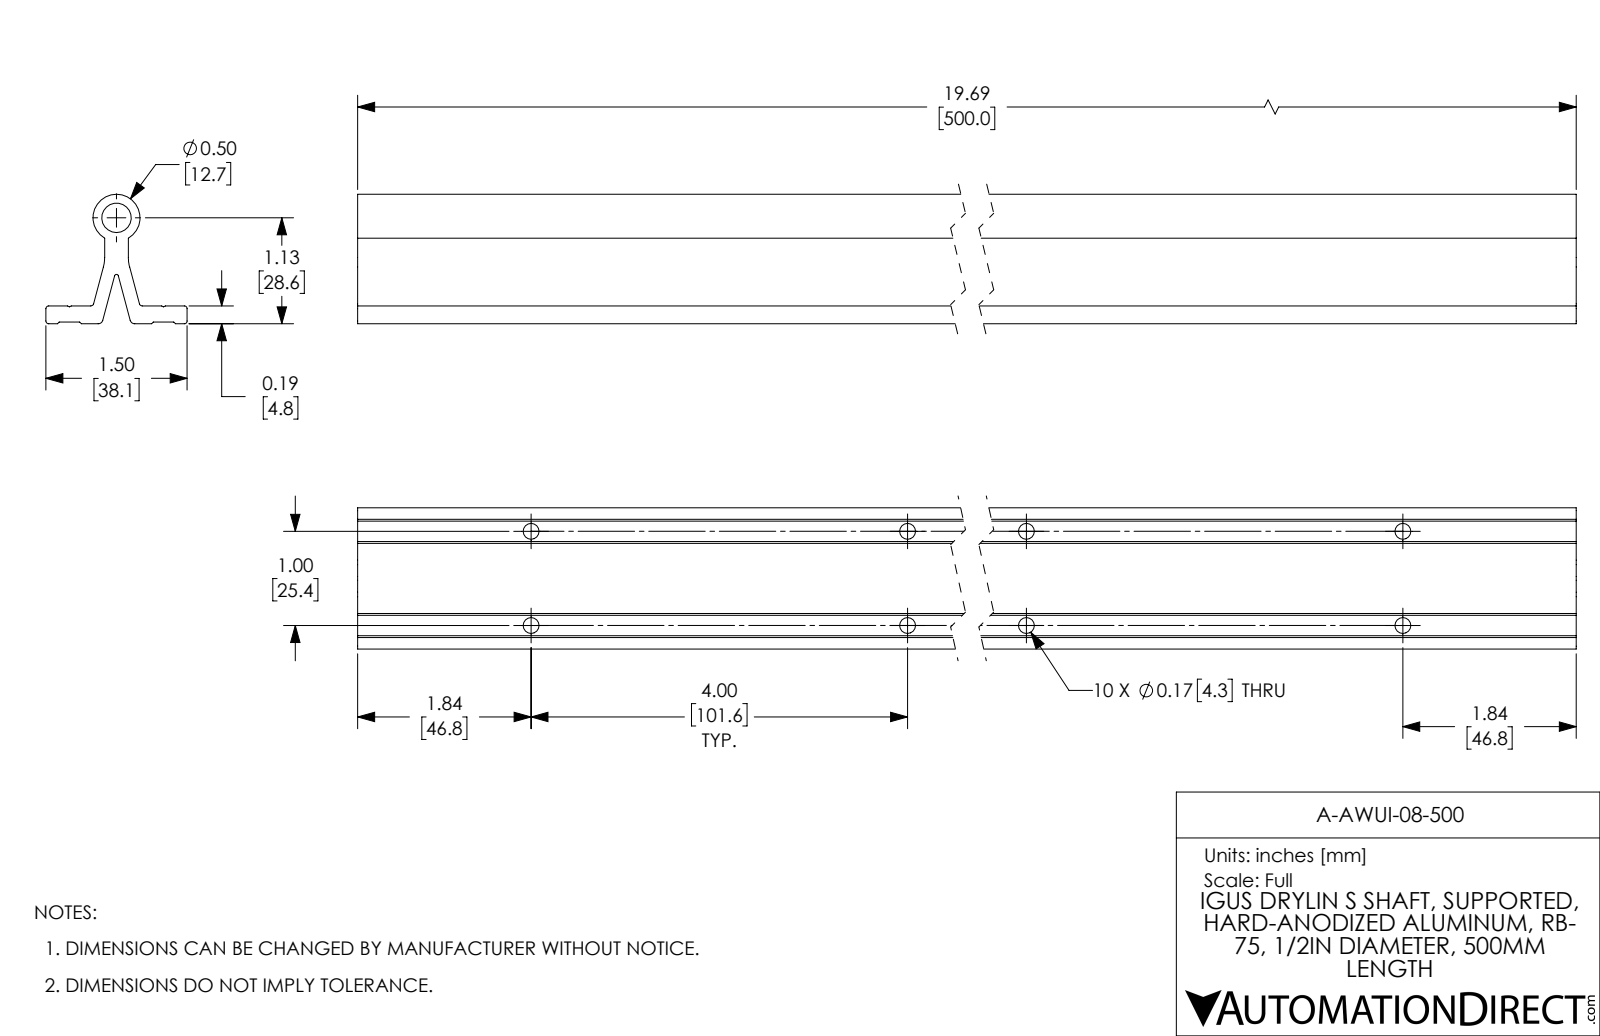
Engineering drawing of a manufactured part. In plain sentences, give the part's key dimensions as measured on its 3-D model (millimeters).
The part is named "A-AWUI-08-500". Its 3-D file was written by "SolidWorks 2017 (AUTOMOTIVE_DESIGN)". It is 1 solid with 82 faces: 48 planar, 34 cylindrical and 0 other. Overall it measures 500 by 38.1 by 34.9 millimeters. Its volume is 172 600 cubic millimeters and its surface area 94 840 square millimeters. Round holes: 10 of diameter 4.3, 1 of diameter 8. Round bosses or shafts: 1 of diameter 12.7. Partial cylindrical surfaces (rounded edges, fillets, slot ends): 6 of radius 0.8, 2 of radius 1.3, 2 of radius 10, 1 of radius 0.5. The main face-to-face distances are 3.6, 4.8, 0.5, 4.3, 15.8, 22.3, 6.4, 38.1, 18, 11.6. The hole center spacings are 101.6, 104.7, 203.2, 204.8, 25.4, 304.8, 305.9, 406.4.
